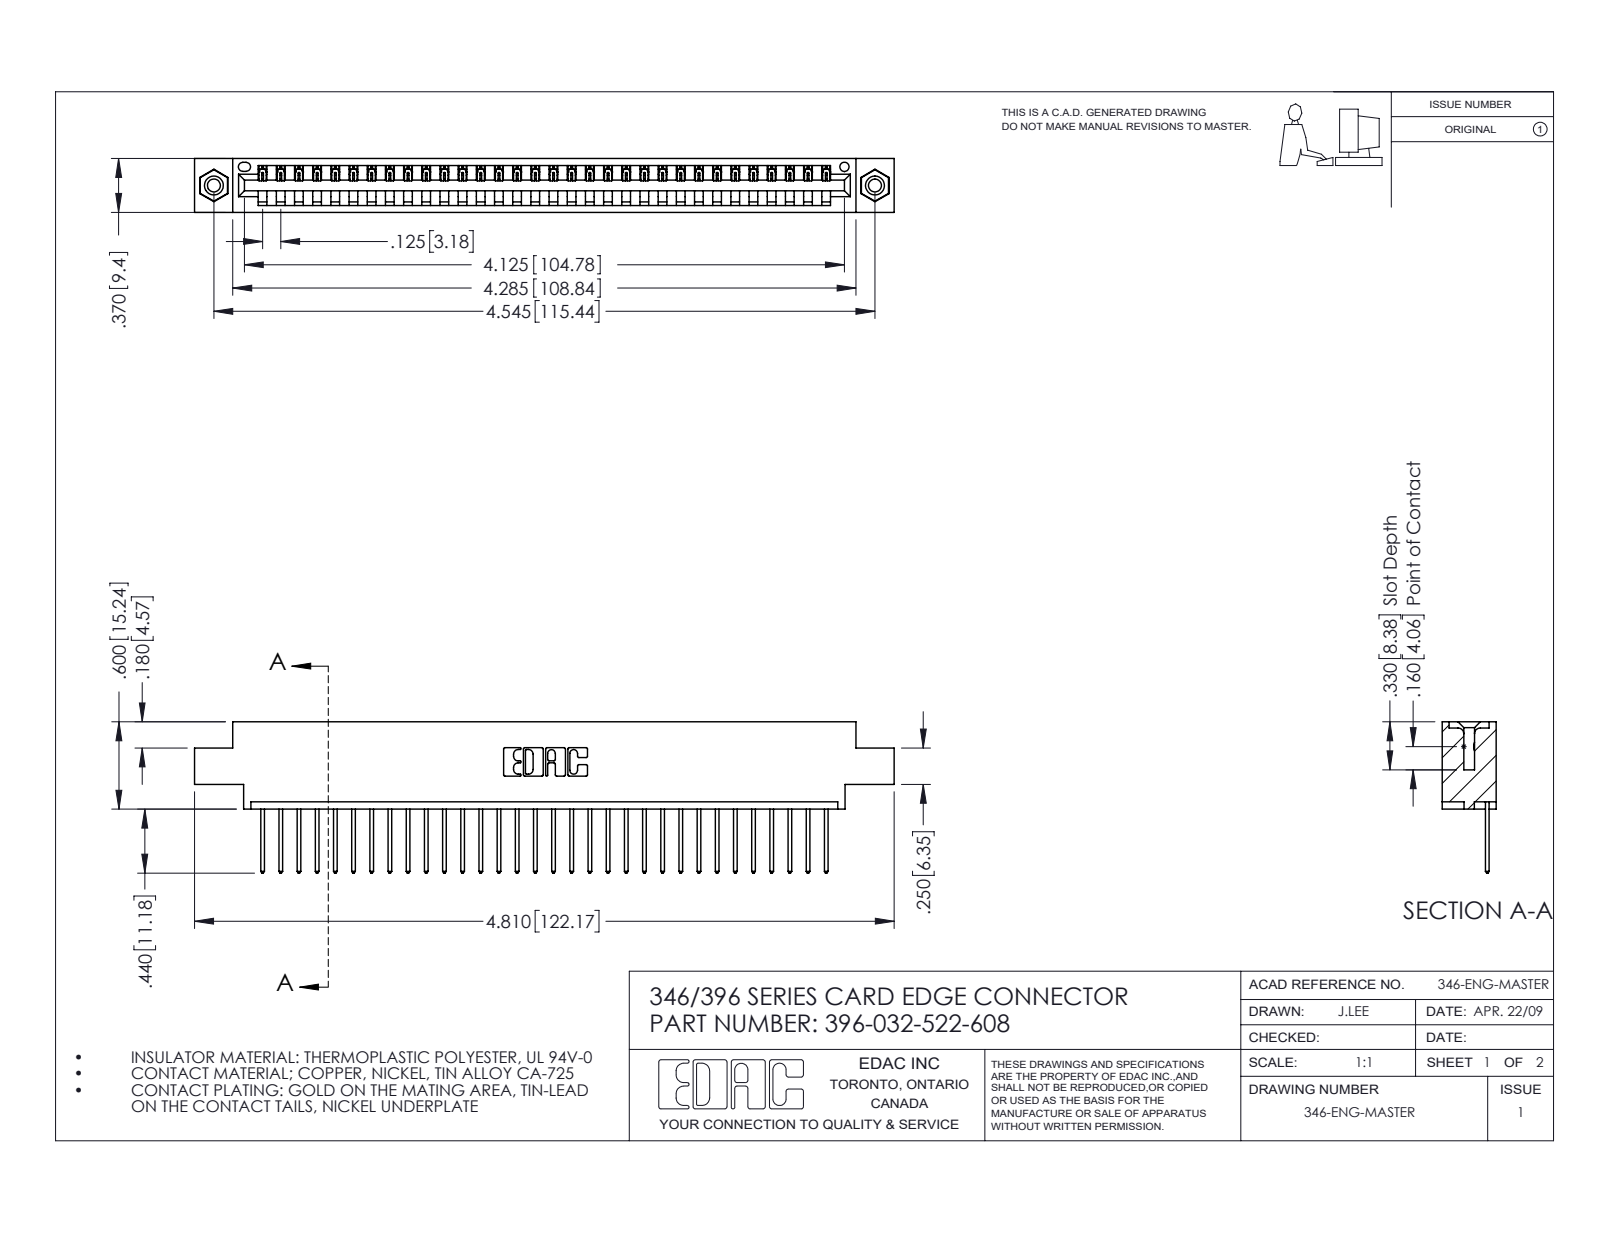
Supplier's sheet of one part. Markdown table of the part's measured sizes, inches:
| quantity | value |
| --- | --- |
| part name | 346 Part_0.170 Offset - 0.156 Dia-TI; 345-292-001_345-293-122; 345-250-001_345-250-003-102; 396-032-522-608 |
| STEP written by | SolidWorks 2016 (CONFIG_CONTROL_DESIGN) |
| units | inches |
| bodies | 35 solids, 2042 faces (1392 planar, 634 cylindrical, 16 other) |
| overall size | 4.81 × 1.04 × 0.37 |
| volume | 0.7 in³ |
| surface area | 22.52 in² |
| round holes (diameter × count) | 0.089 × 2, 0.125 × 2, 0.156 × 2, 0.064 × 1 |
| round bosses / shafts (diameter × count) | 0.155 × 2 |
| partial cylindrical surfaces (radius × count) | 0.006 × 64, 0.01 × 64, 0.01 × 22, 0.007 × 6, 0.031 × 6, 0.026 × 3, 0.031 × 2, 0.04 × 2 |
| main face-to-face distances | 0.048, 0.322, 0.37, 0.25, 0.072, 0.298, 0.025, 0.222, 0.148, 0.1 |
| hole center spacings | 0.246, 4.337, 4.545 |
